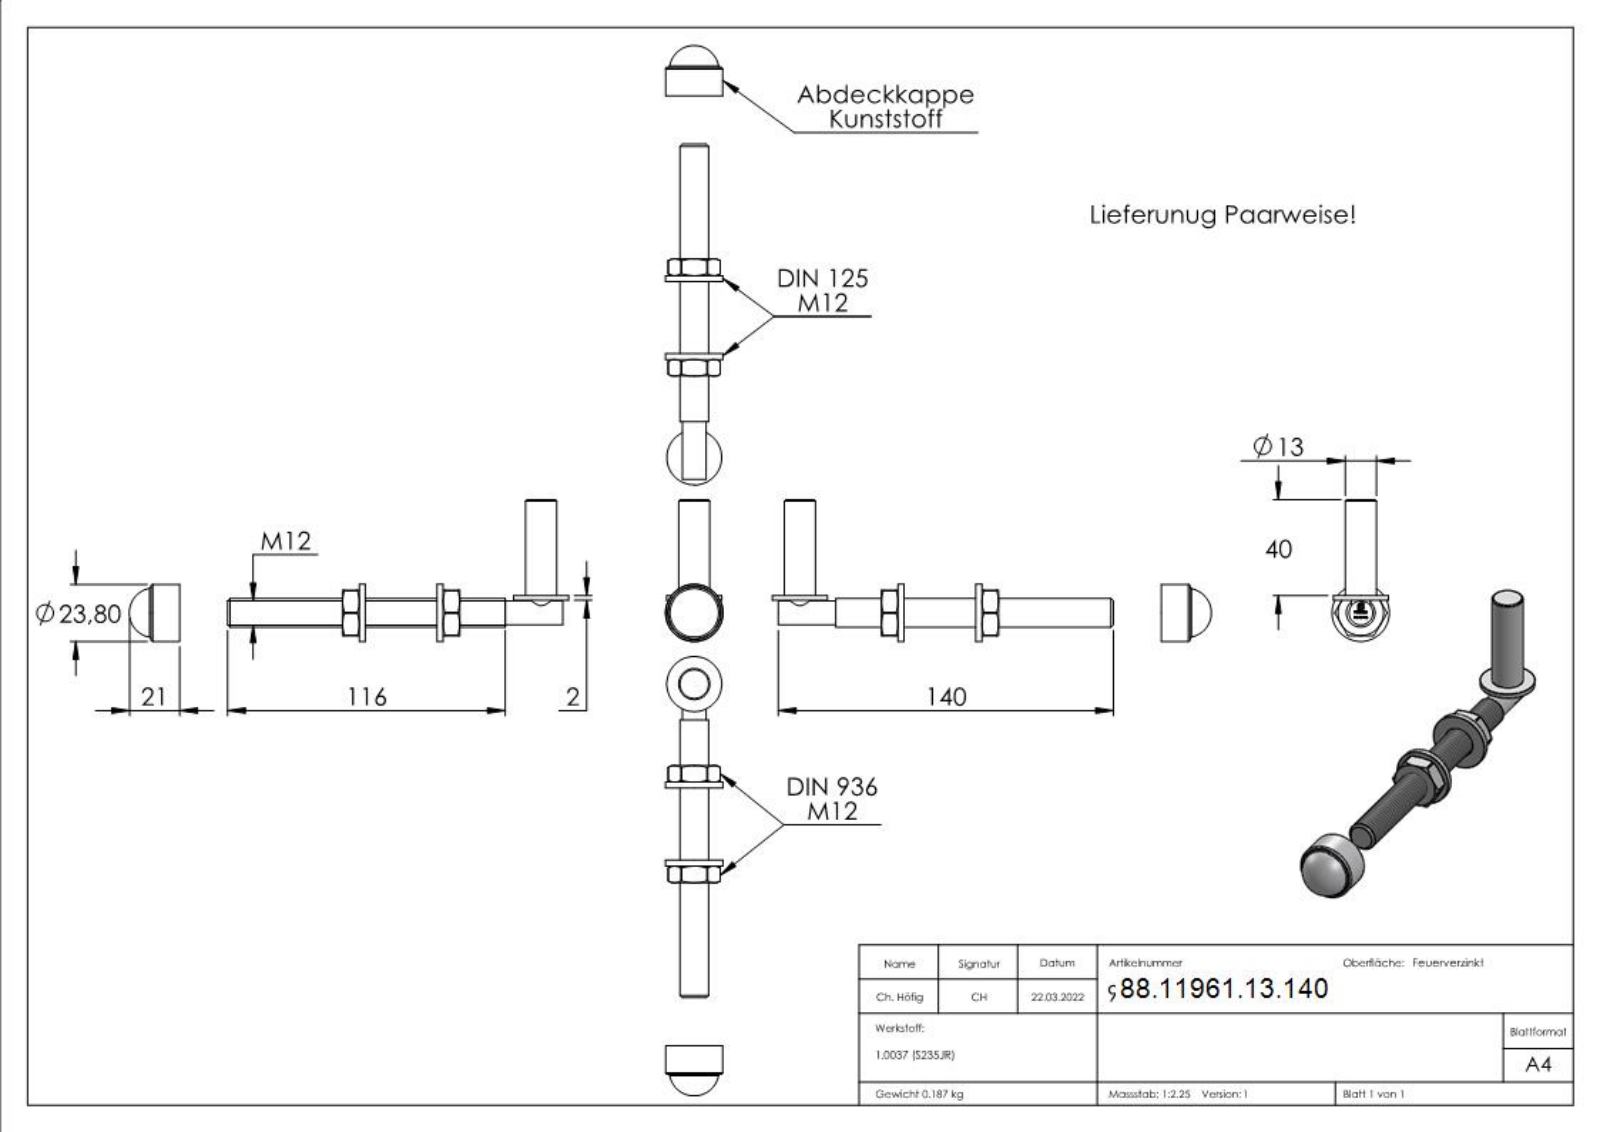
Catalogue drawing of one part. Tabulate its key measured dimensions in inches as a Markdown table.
| quantity | value |
| --- | --- |
| part name | 961-13-140; 961-1X-XXX Teil2_961-XX-XXX Teil2; DIN 936 M8-M24_DIN 936 M12; 961-1X-XXX Teil1_961-13-140 Teil1 (+1 more) |
| STEP written by | SolidWorks 2018 (CONFIG_CONTROL_DESIGN) |
| units | inches |
| bodies | 6 solids, 358 faces (190 planar, 25 cylindrical, 143 other) |
| overall size | 7.224 × 2.331 × 0.945 |
| volume | 1.707 in³ |
| surface area | 23.11 in² |
| round holes (diameter × count) | 0.402 × 1, 0.512 × 1, 0.748 × 1 |
| round bosses / shafts (diameter × count) | 0.945 × 1, 0.937 × 1, 0.906 × 1, 0.512 × 1, 0.472 × 1, 0.394 × 1, 0.315 × 1 |
| partial cylindrical surfaces (radius × count) | 0.02 × 6 |
| main face-to-face distances | 0.748, 0.098, 1.28, 1.378, 1.654, 0.374, 0.276, 1.555, 1.181, 0.079 |
